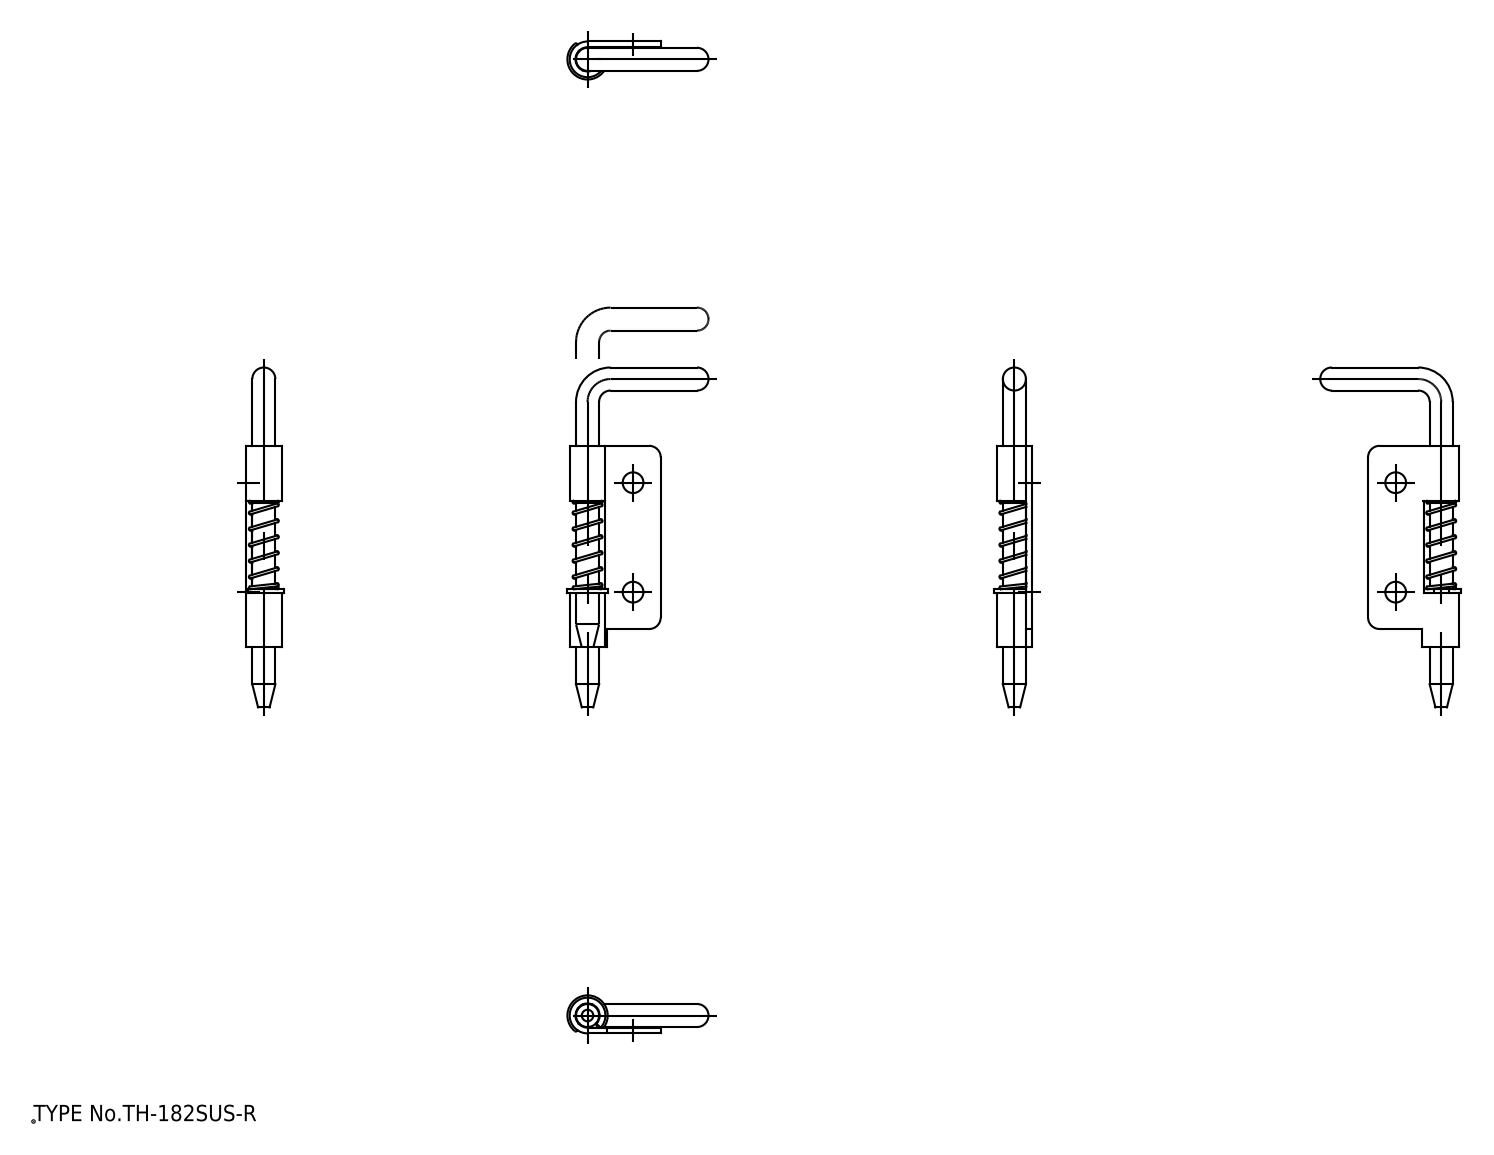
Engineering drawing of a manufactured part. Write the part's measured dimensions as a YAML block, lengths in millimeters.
part_name: "シャフト; スプリング_M2; ヒンジピース"
step_written_by: "spGate 18.9.1 (****-****-****-****) (AUTOMOTIVE_DESIGN)"
units: millimeters
bodies: {solids: 3, faces: 87, planar: 27, cylindrical: 27, other: 33}
overall_size: [59, 24.5, 6.6]
volume: 1572
surface_area: 2582
round_holes:
  - {diameter: 3.6, count: 2}
  - {diameter: 4.2, count: 1}
round_bosses_or_shafts:
  - {diameter: 4, count: 2}
  - {diameter: 6.2, count: 1}
  - {diameter: 3.05, count: 1}
partial_cylinders:
  - {radius: 0.25, count: 6}
  - {radius: 2, count: 2}
  - {radius: 2.6, count: 1}
  - {radius: 3.5, count: 1}
face_to_face_distances: [1, 25.5, 9.5, 0.6, 24.9, 10.1, 35, 16, 15.4, 9.7]
hole_center_spacings: [19]
